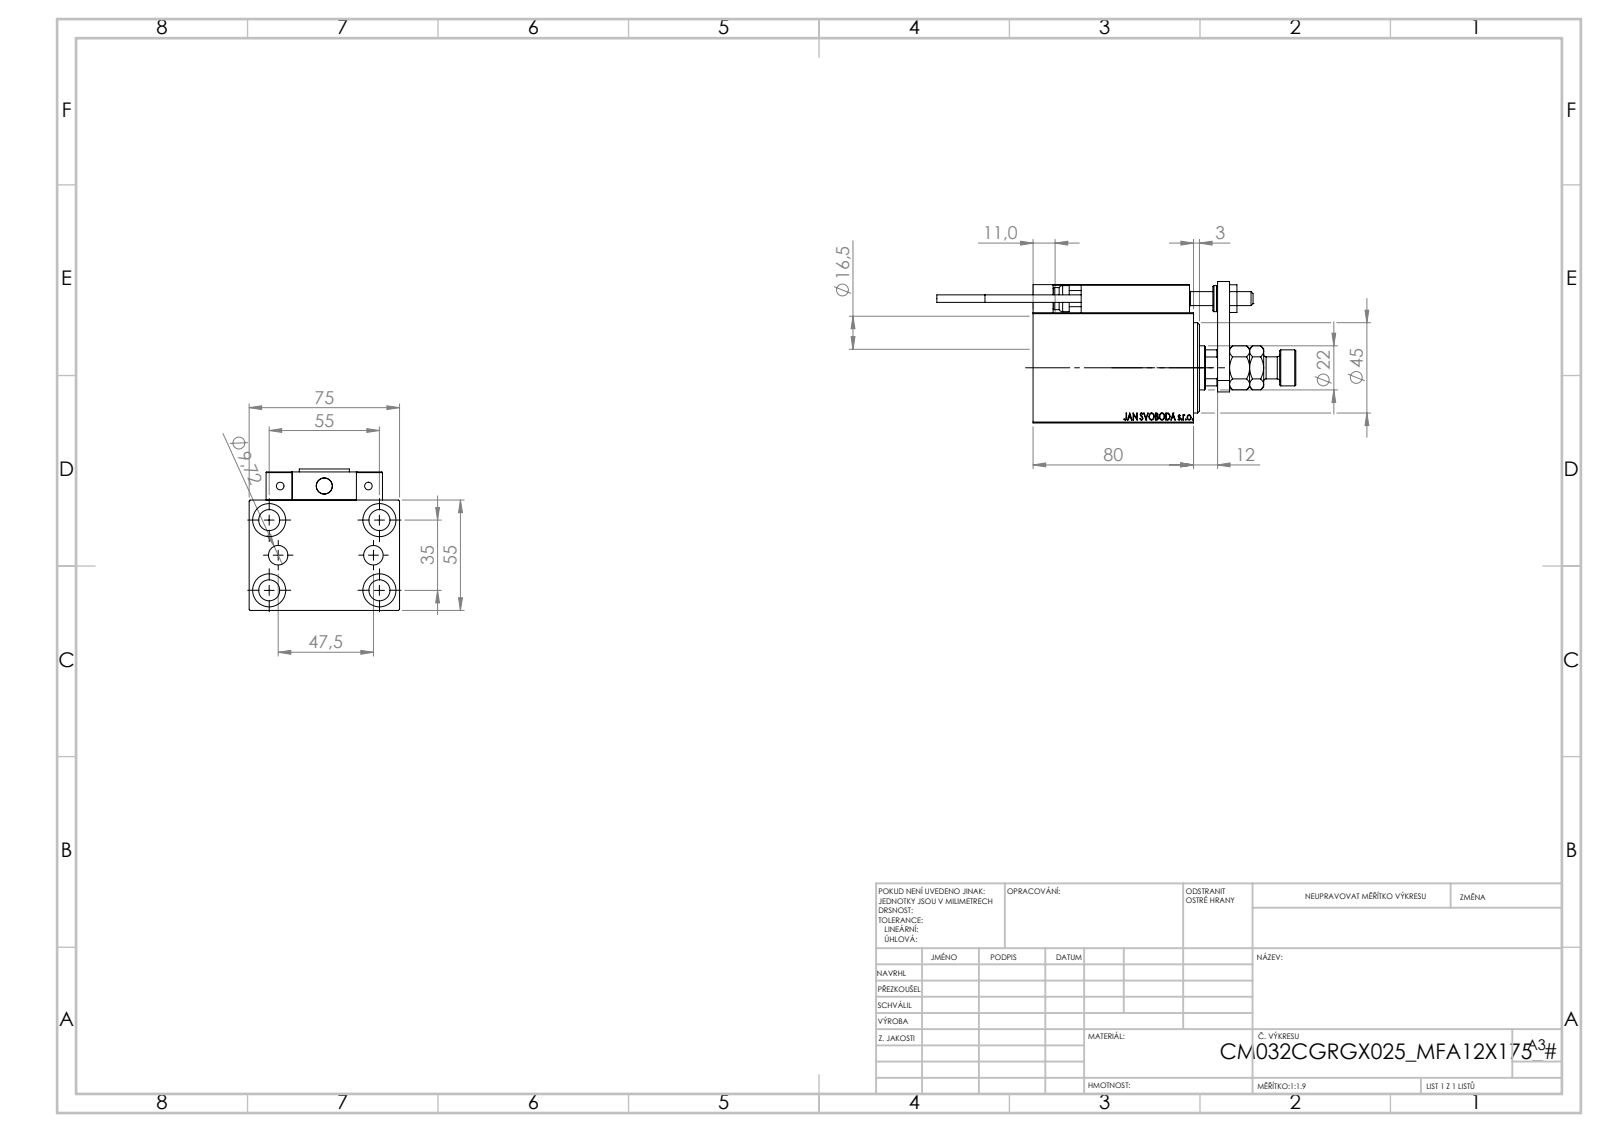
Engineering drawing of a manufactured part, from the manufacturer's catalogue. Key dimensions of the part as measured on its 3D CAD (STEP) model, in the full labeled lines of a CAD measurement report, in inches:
Part name (STEP PRODUCT): NUT_D12; Block; V450CM_C_Body; ALLEN BOLT D8 (+8 more)
STEP written by: SolidWorks 2019 (CONFIG_CONTROL_DESIGN)
Units: inches
Bodies: 24 solids, 1330 faces (576 planar, 188 cylindrical, 566 other)
Overall size (bounding box): 7.047 × 2.953 × 2.776
Volume: 20.68 in³ · Surface area: 135.3 in²
Round holes (diameter × count): ⌀0.157 ×6, ⌀0.315 ×5, ⌀0.413 ×5, ⌀0.65 ×5, ⌀0.126 ×4, ⌀0.197 ×2, ⌀0.383 ×2, ⌀0.276 ×1, ⌀0.866 ×1, ⌀1.004 ×1, ⌀1.26 ×1, ⌀1.339 ×1
Round bosses / shafts (diameter × count): ⌀0.433 ×2, ⌀0.197 ×2, ⌀0.15 ×2, ⌀0.709 ×1, ⌀0.512 ×1
Partial cylindrical surfaces — rounded edges, fillets, slot ends (radius × count): R0.012 ×30, R0.118 ×2, R0.413 ×1
Main face-to-face distances: 2.165, 2.953, 0.551, 2.717, 0.906, 0.197, 0.984, 0.118, 0.394, 0.709
Hole centre spacings: 0.705, 1.283, 2.132, 0.448, 0.787, 0.935, 1.165, 1.169
